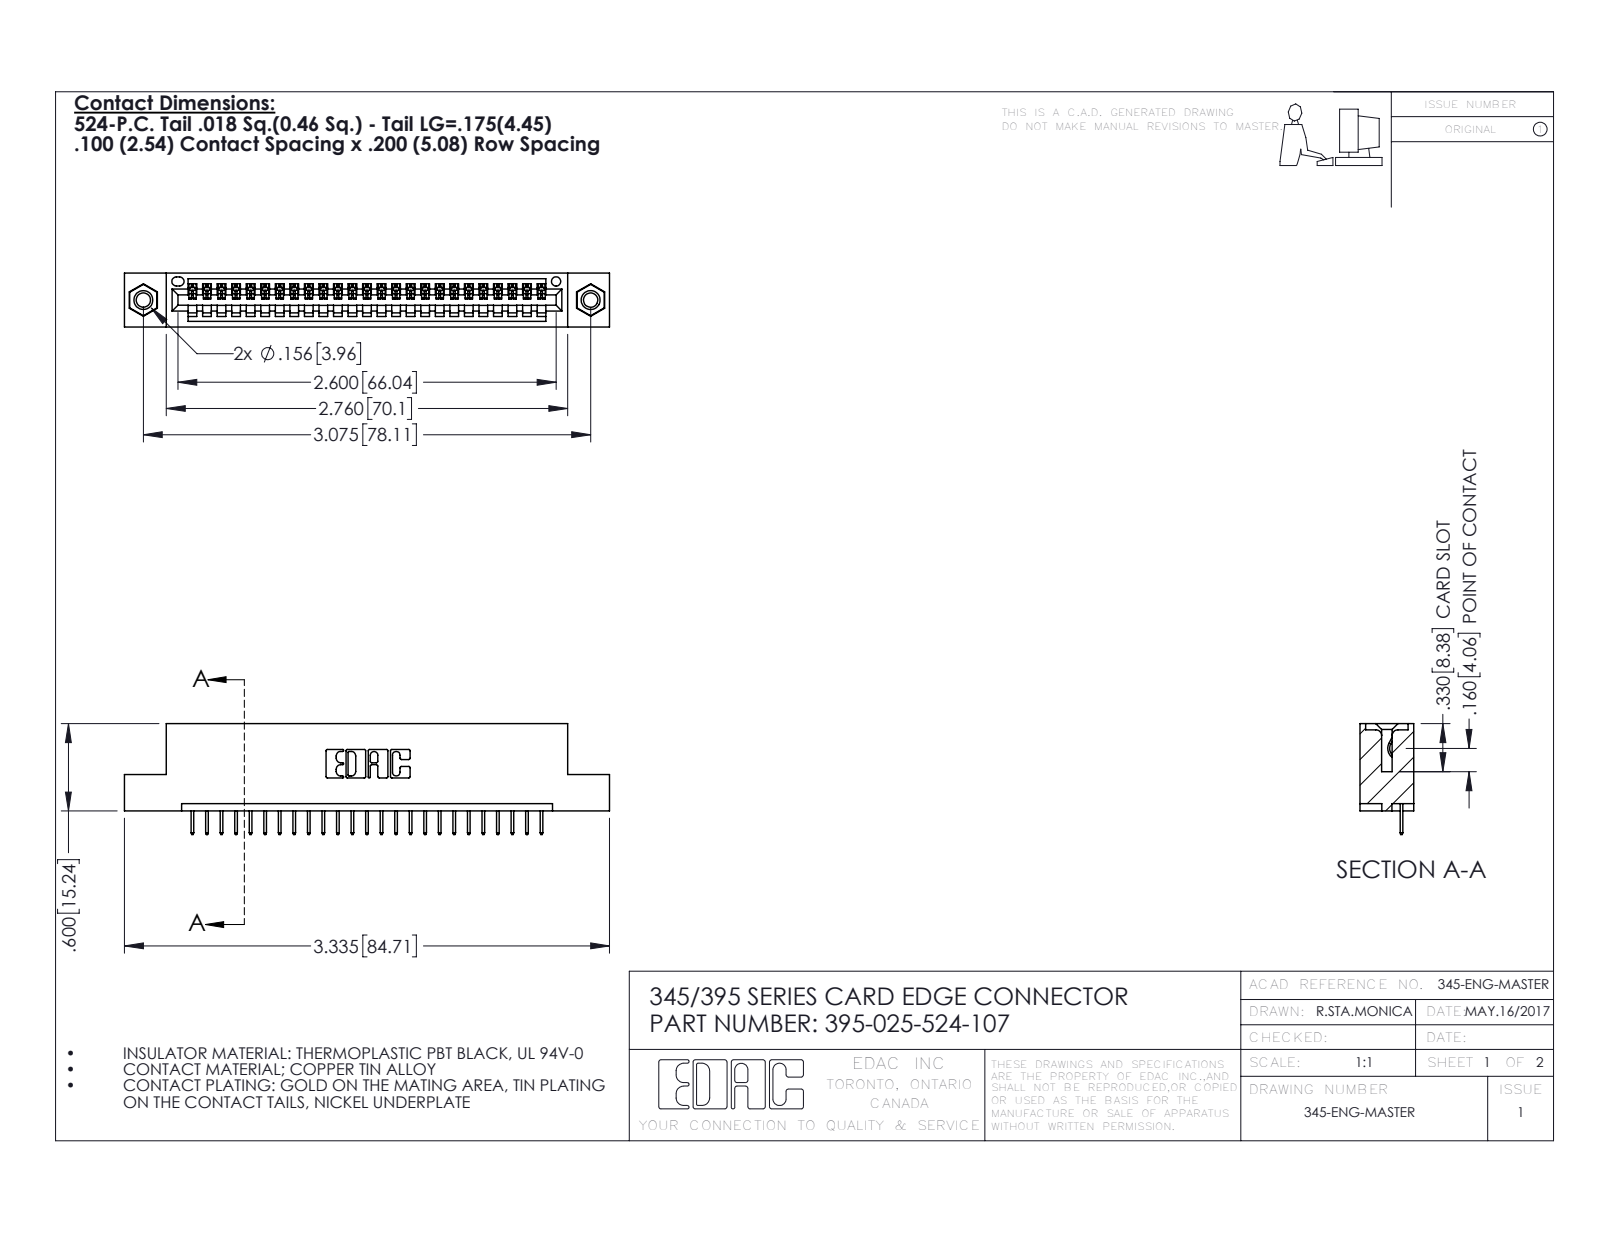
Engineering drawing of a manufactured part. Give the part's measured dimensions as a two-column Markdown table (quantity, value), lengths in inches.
| quantity | value |
| --- | --- |
| part name | 395-025-524-107; 345-250-001_345-250-005-103; 345-292-001_345-293-124; 345 Part_Flush Mounting Lugs - 0.156 Dia-TI |
| STEP written by | SolidWorks 2016 (CONFIG_CONTROL_DESIGN) |
| units | inches |
| bodies | 28 solids, 1736 faces (1262 planar, 458 cylindrical, 16 other) |
| overall size | 3.335 × 0.762 × 0.37 |
| volume | 0.476 in³ |
| surface area | 15.26 in² |
| round holes (diameter × count) | 0.098 × 2, 0.125 × 2, 0.156 × 2, 0.064 × 1 |
| round bosses / shafts (diameter × count) | 0.155 × 2 |
| partial cylindrical surfaces (radius × count) | 0.006 × 50, 0.01 × 22, 0.007 × 6, 0.031 × 6, 0.026 × 3, 0.031 × 2, 0.04 × 2, 0.014 × 1 |
| main face-to-face distances | 0.072, 0.298, 0.37, 0.2, 0.098, 0.272, 0.025, 0.225, 0.072, 0.149 |
| hole center spacings | 0.27, 2.84, 3.075 |
